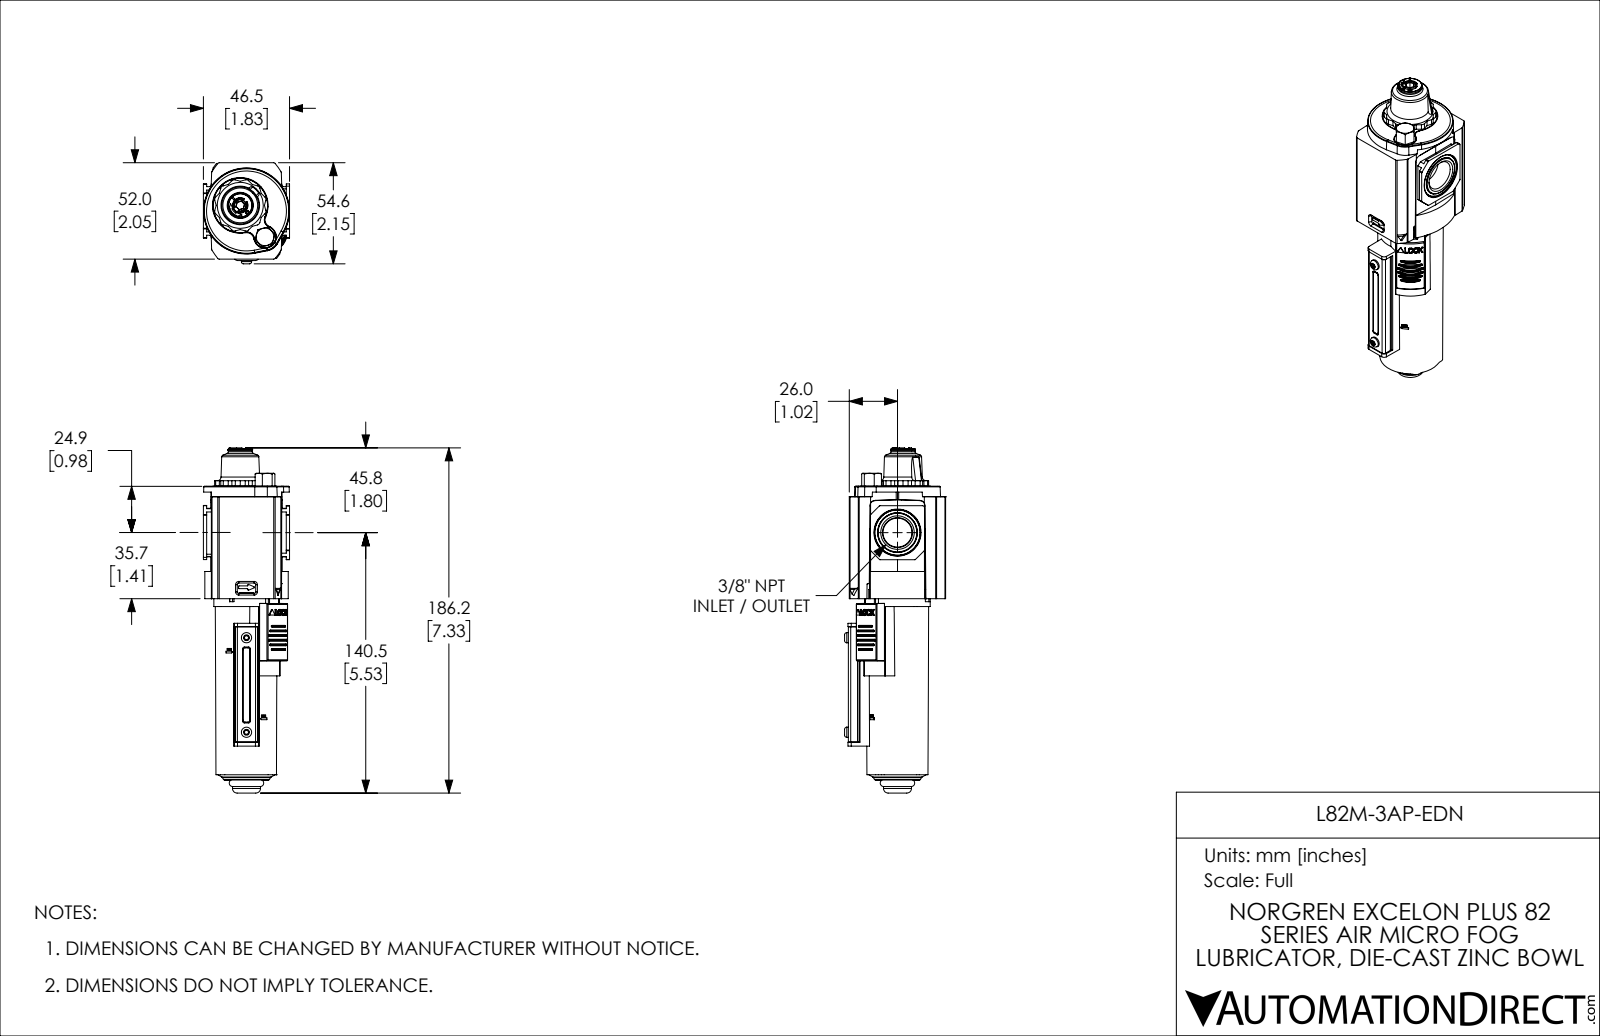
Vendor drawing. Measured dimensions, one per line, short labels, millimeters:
name: L82M-3AP-EDN
written by: SolidWorks 2021 (CONFIG_CONTROL_DESIGN)
unit: mm
bodies: 7 solids, 1276 faces (576 planar, 469 cylindrical, 231 other)
size: 186.2 × 54.6 × 46.5
volume: 204 800 mm³; area: 61 830 mm²
holes: 1× ⌀6.9, 1× ⌀7.9, 1× ⌀7.9, 1× ⌀9, 1× ⌀16, 1× ⌀24, 1× ⌀30
bosses: 2× ⌀6.1, 2× ⌀5.5, 1× ⌀35.3, 1× ⌀34.4, 1× ⌀32.8, 1× ⌀31.9, 1× ⌀29.5, 1× ⌀23
rounds: 53× R0.5, 38× R1, 16× R0.2, 12× R0.3, 12× R0.3, 12× R0.5, 12× R1.9, 9× R3
face distances: 1.5, 50.5, 52, 49, 6, 34.3, 4.6, 37.5, 36, 32.8
hole spacings: 4.5, 17.2, 21.6
